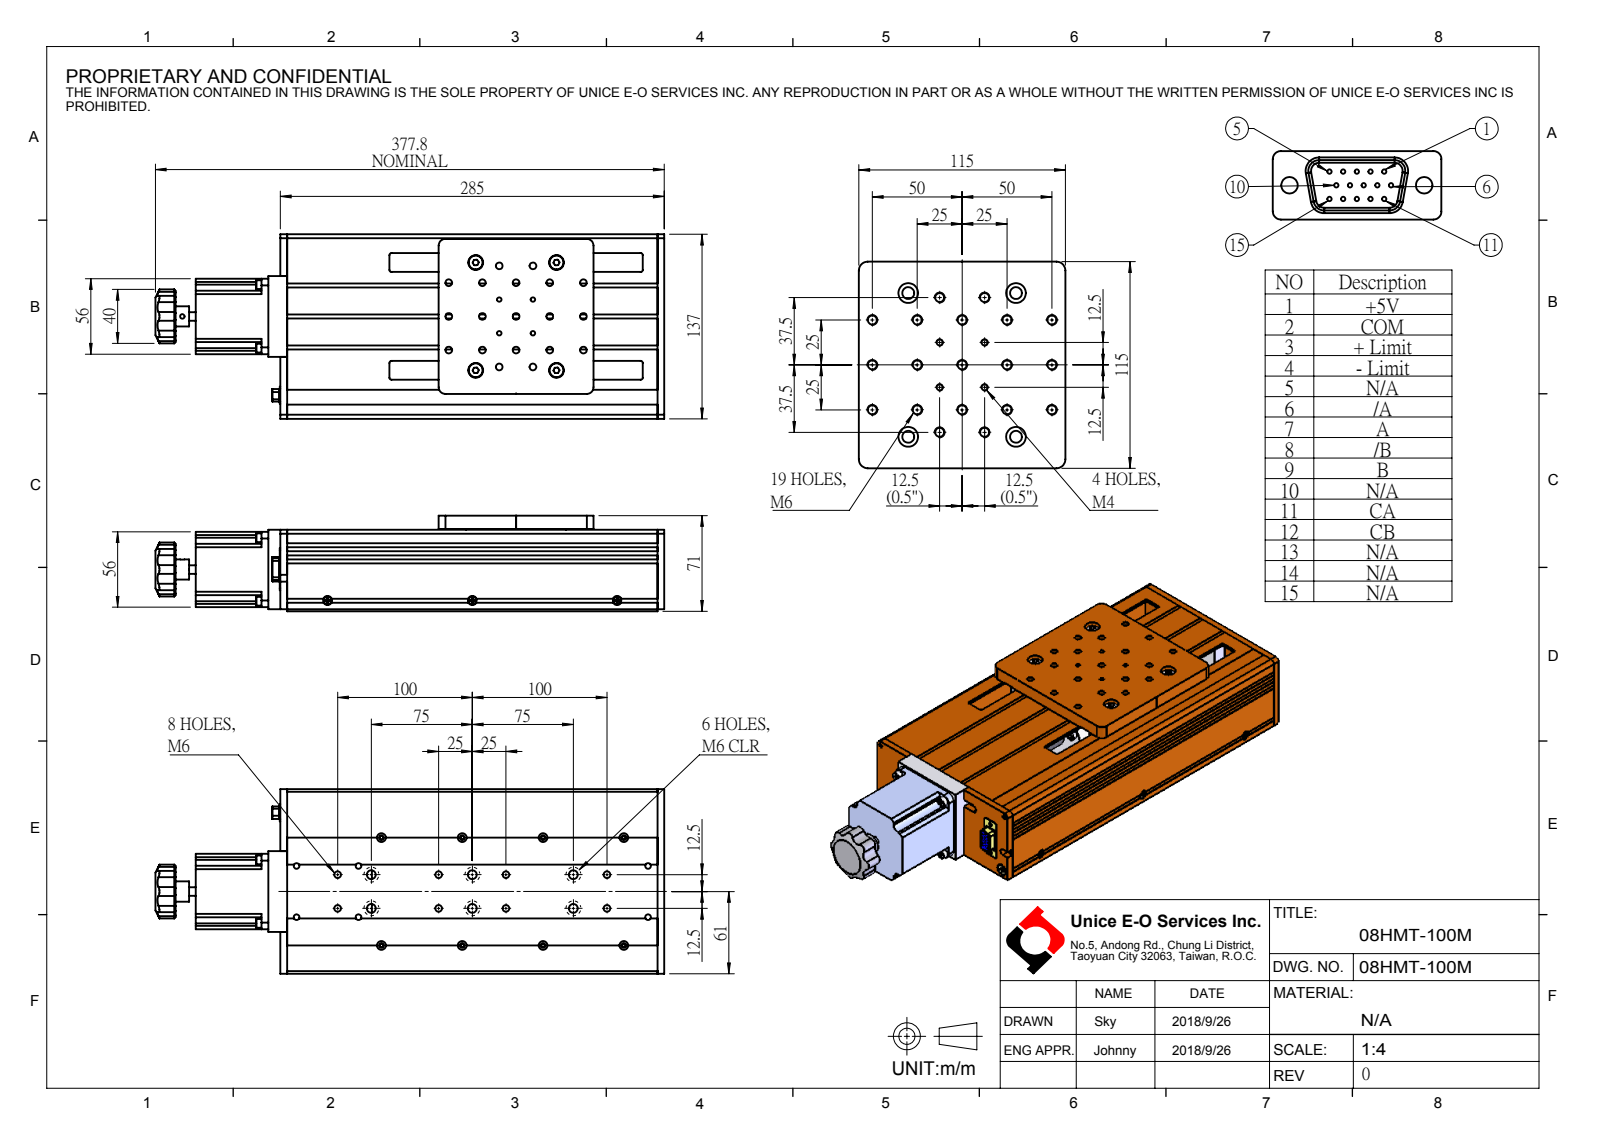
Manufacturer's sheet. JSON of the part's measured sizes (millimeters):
{"part_name": "08HMT-100M", "step_written_by": "SolidWorks 2016 (AUTOMOTIVE_DESIGN)", "units": "millimeters", "bodies": {"solids": 0, "faces": 760, "planar": 363, "cylindrical": 281, "other": 116}, "overall_size": [377.8, 137, 71], "round_holes": [[5, 27], [0.8, 14], [6.5, 8], [11, 7], [3.3, 6], [4.2, 6], [6.6, 6], [2, 2], [2.26, 2], [3.05, 2], [25, 1]], "round_bosses_or_shafts": [[6.5, 4], [5.8, 3], [7.7, 2], [7, 2], [15, 1], [14, 1], [6.35, 1]], "partial_cylinders_radius": [[1.5, 12], [0.5, 8], [4, 8], [5, 8], [7.41, 8], [2, 4], [4.5, 4], [3, 3]], "face_to_face_distances": [2, 60.5, 135, 133, 1.5, 10.5, 59, 137, 5, 71], "hole_center_spacings": [25, 2.84, 100, 5.08, 4.58, 2.54, 5.68, 6.84]}
